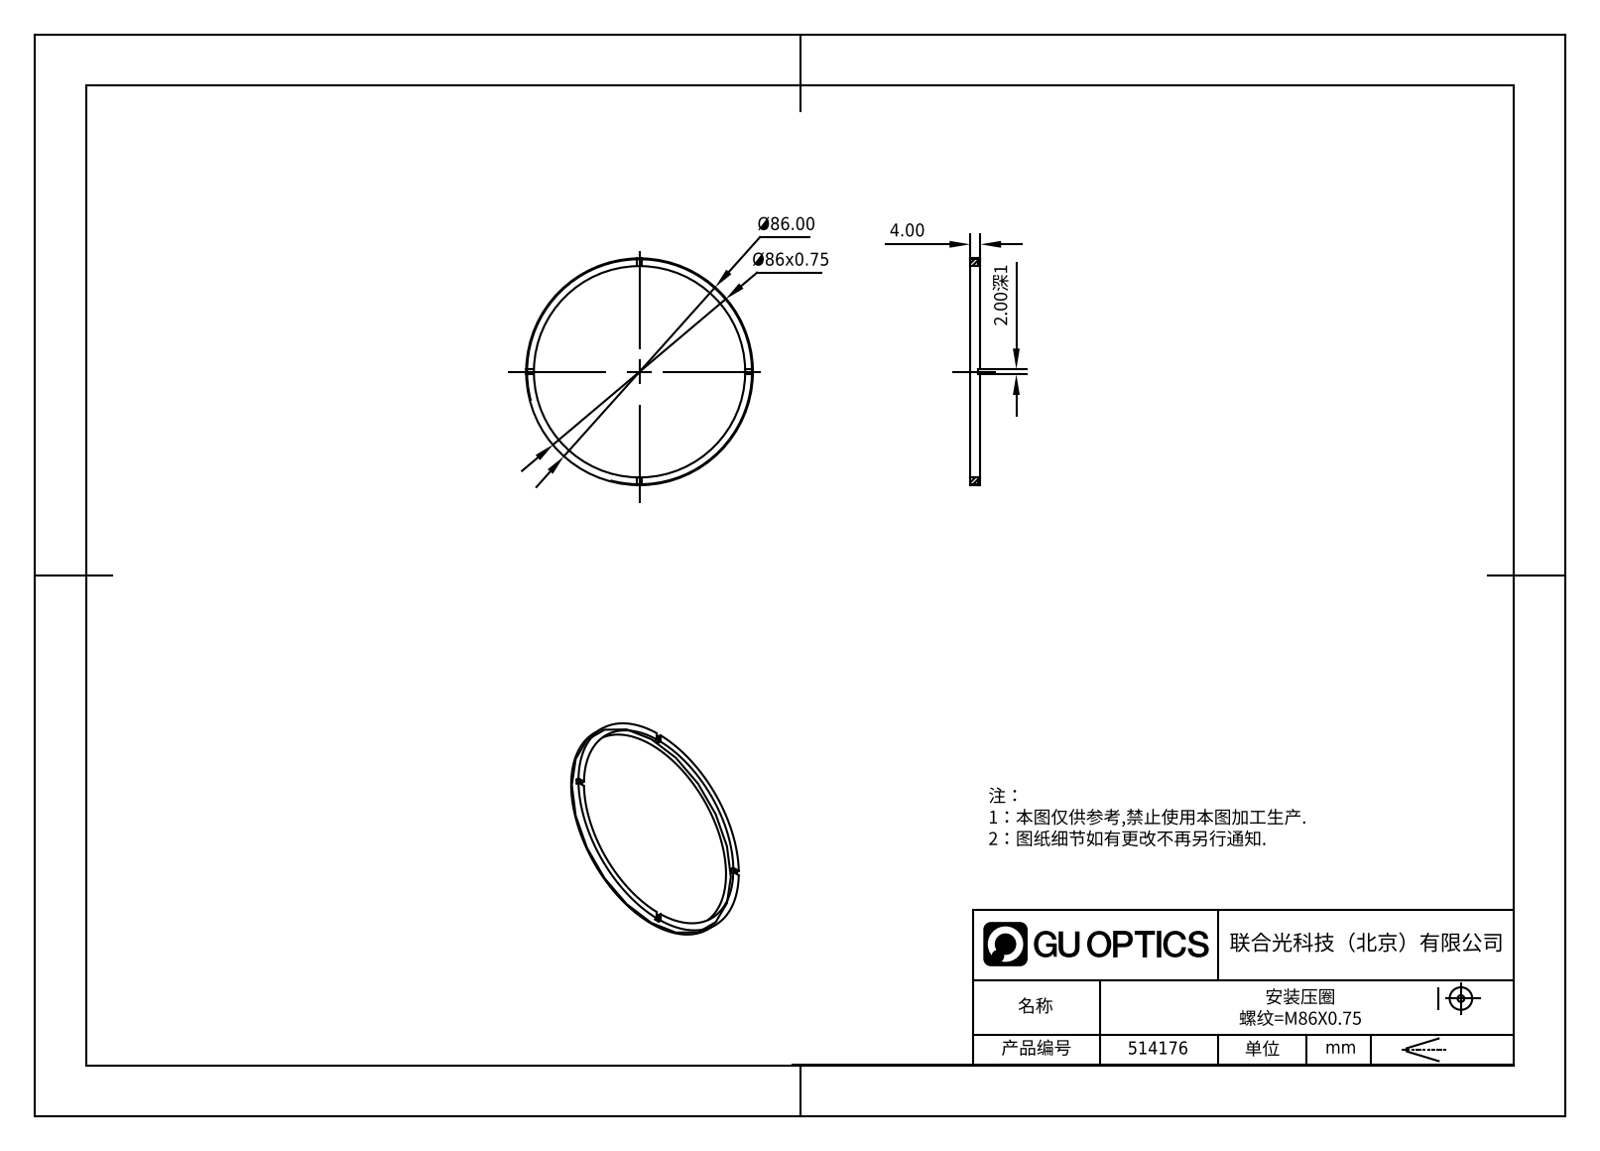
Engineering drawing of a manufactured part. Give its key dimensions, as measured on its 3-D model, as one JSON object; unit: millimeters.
{"part_name": "514176", "step_written_by": "SolidWorks 2020 (CONFIG_CONTROL_DESIGN)", "units": "millimeters", "bodies": {"solids": 1, "faces": 21, "planar": 17, "cylindrical": 4, "other": 0}, "overall_size": [86, 86, 4], "volume_mm3": 3105, "surface_area_mm2": 3659, "round_holes": [[80, 1]], "round_bosses_or_shafts": [[86, 1]], "face_to_face_distances": [4, 3, 1, 2]}
